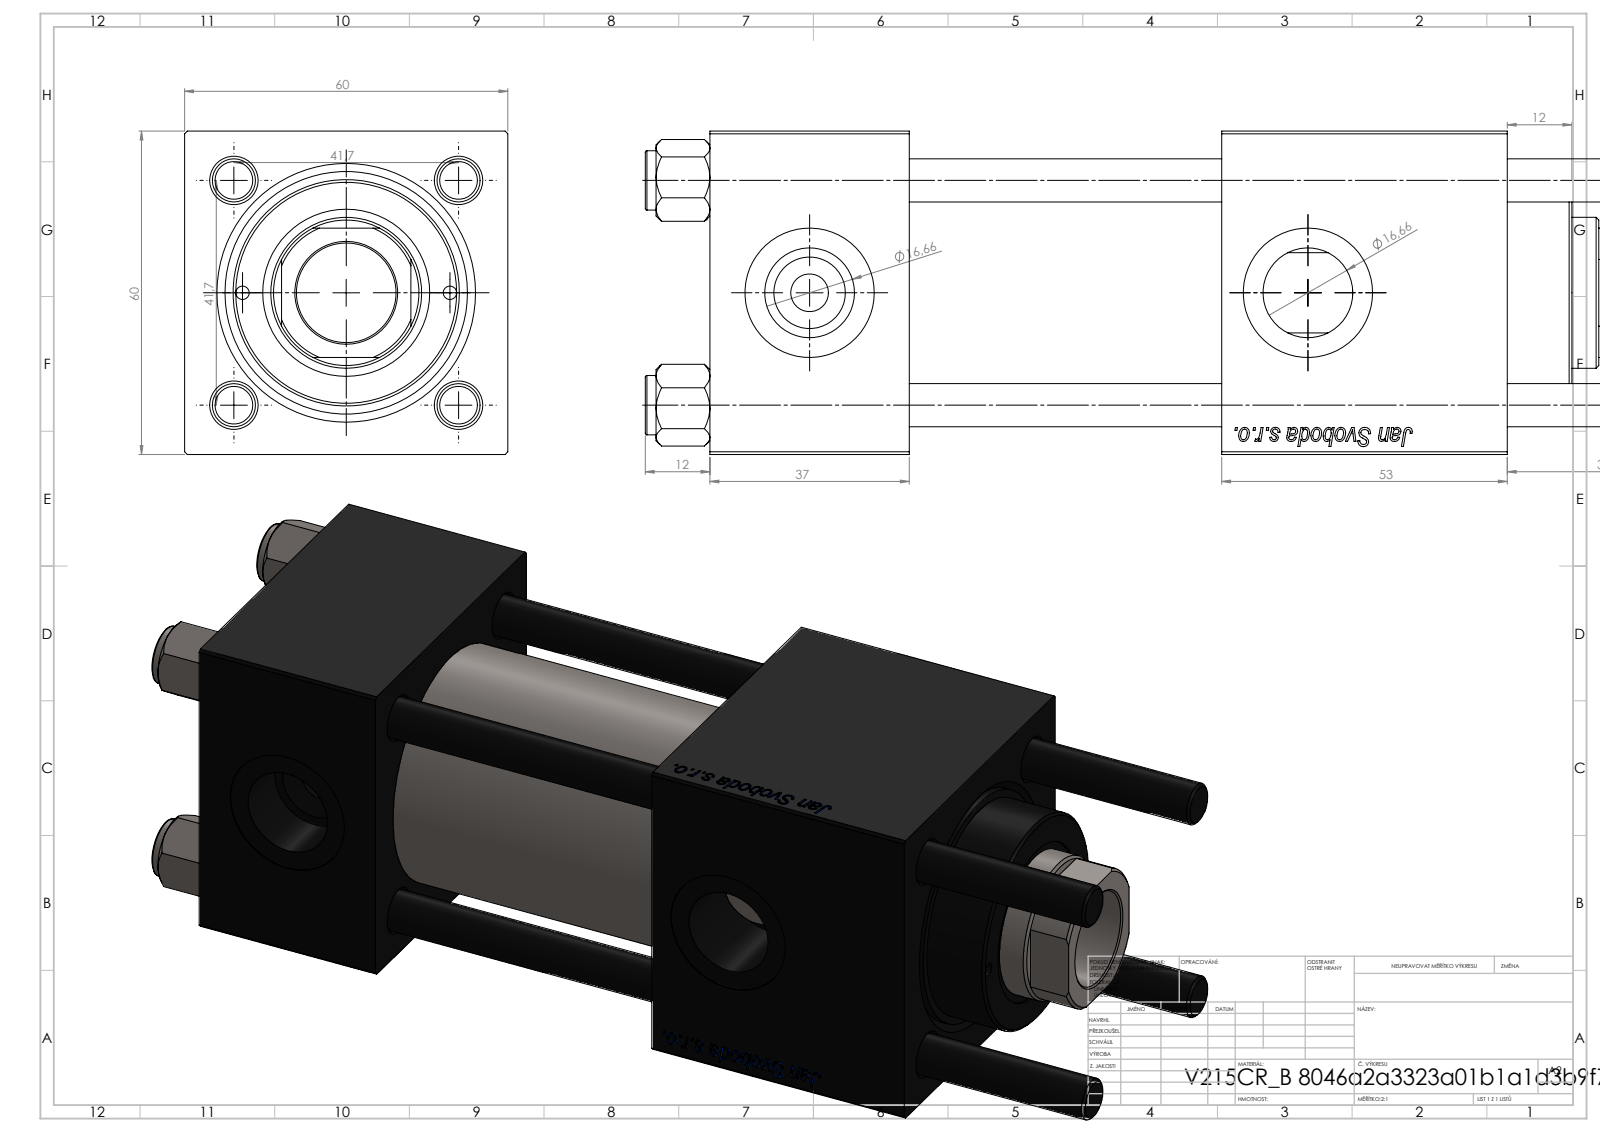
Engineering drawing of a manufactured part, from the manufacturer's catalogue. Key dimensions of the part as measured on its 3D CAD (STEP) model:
Part name (STEP PRODUCT): V215CR_B_TYCINKA; V215CR_B-1; NUT_M5_B; V215CR_VCP_B (+1 more)
STEP written by: SolidWorks 2019 (CONFIG_CONTROL_DESIGN)
Units: millimetres
Bodies: 11 solids, 1165 faces (435 planar, 82 cylindrical, 648 other)
Overall size (bounding box): 195 × 60 × 60
Volume: 435 407 mm³ · Surface area: 120 123 mm²
Round holes (diameter × count): ⌀8 ×4, ⌀2.5 ×2, ⌀7 ×2, ⌀16.66 ×2, ⌀24 ×2, ⌀18.5 ×1, ⌀28 ×1, ⌀31 ×1, ⌀40 ×1, ⌀45 ×1
Round bosses / shafts (diameter × count): ⌀11 ×4, ⌀46 ×1, ⌀42 ×1
Partial cylindrical surfaces — rounded edges, fillets, slot ends (radius × count): R13.5 ×1
Main face-to-face distances: 60, 37, 58, 95, 119.3, 82.3, 24.3, 53, 148, 111
Hole centre spacings: 20.91, 29.49, 41.7, 45.2, 19.25, 58.97, 38.5, 92.5
